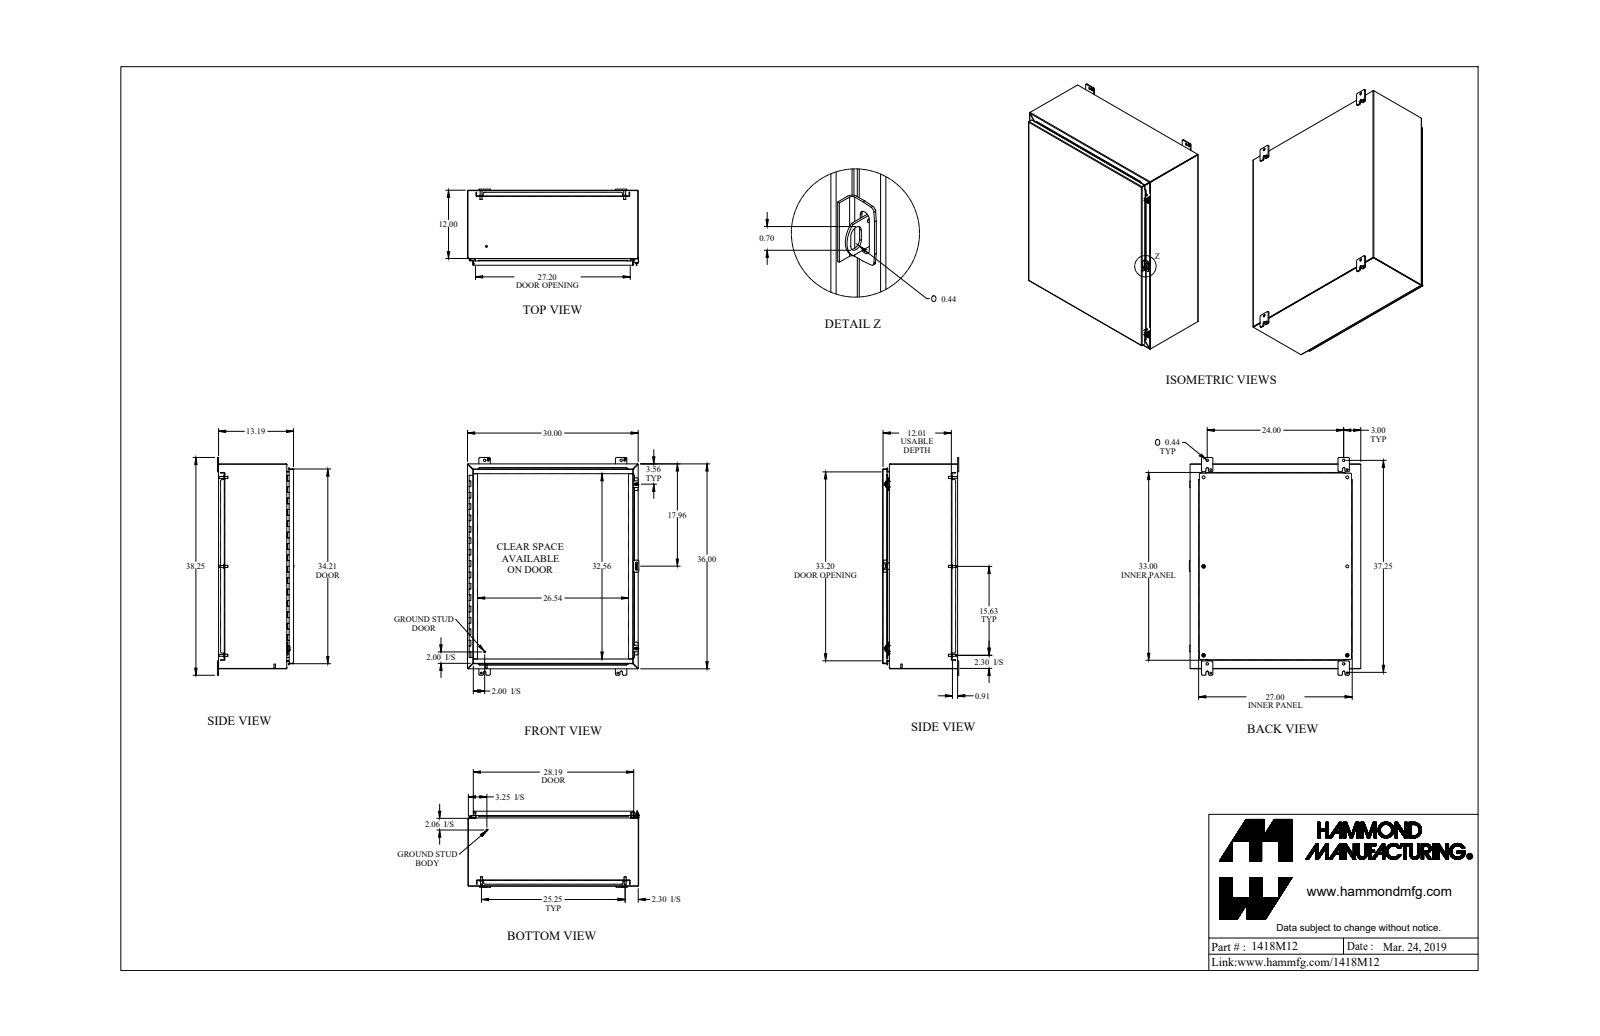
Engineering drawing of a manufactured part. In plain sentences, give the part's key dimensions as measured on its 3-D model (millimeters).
The part is named "1418M12_Default". Its 3-D file was written by "SolidWorks 2019 (CONFIG_CONTROL_DESIGN)". It is 49 solids with 1431 faces: 837 planar, 502 cylindrical and 92 other. Overall it measures 971.6 by 765.2 by 341.3 millimeters. Its volume is 6 965 000 cubic millimeters and its surface area 7 146 000 square millimeters. Round holes: 6 of diameter 12.7, 4 of diameter 7.8, 4 of diameter 8, 4 of diameter 11.1, 4 of diameter 11.3, 2 of diameter 5.4, 2 of diameter 6.7, 2 of diameter 9.5, 1 of diameter 3.2, 1 of diameter 4.7. Round bosses or shafts: 6 of diameter 16.5, 6 of diameter 9.5, 6 of diameter 8.4, 4 of diameter 25.4, 2 of diameter 12.7, 2 of diameter 9.9, 2 of diameter 7.1, 2 of diameter 6.4. Partial cylindrical surfaces (rounded edges, fillets, slot ends): 36 of radius 4.8, 22 of radius 0.9, 22 of radius 2.7, 20 of radius 6.4, 13 of radius 1.2, 13 of radius 3.6, 12 of radius 2.9, 8 of radius 1. The main face-to-face distances are 1.8, 333.1, 331.2, 334.9, 2.4, 23.8, 25.6, 306.9, 305, 26.2. The hole center spacings are 641.4, 396.9, 609.6, 754.2, 1093.7, 696, 793.8, 793.8.
